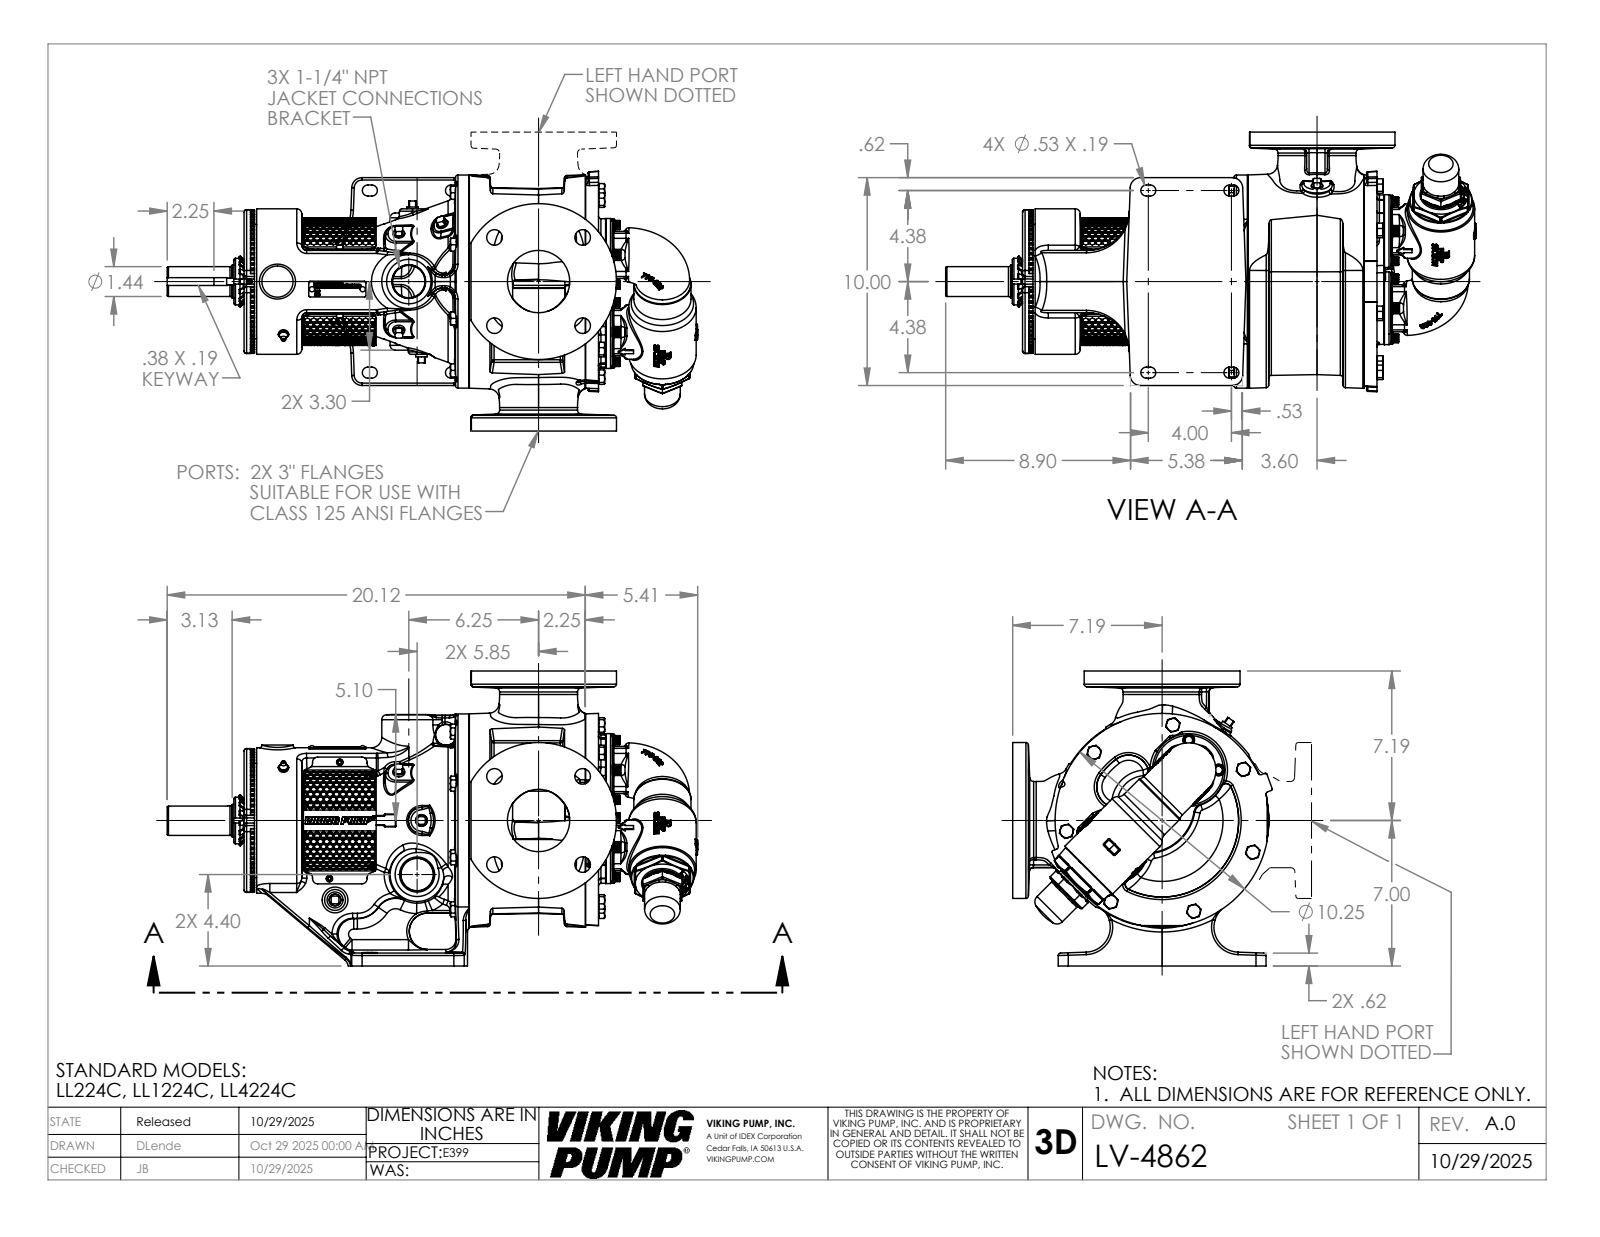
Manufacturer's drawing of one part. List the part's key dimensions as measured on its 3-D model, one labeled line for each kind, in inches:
Part name (STEP PRODUCT): LV-4862
STEP written by: SolidWorks 2024 (AUTOMOTIVE_DESIGN)
Units: inches
Bodies: 1 solid, 5315 faces (1761 planar, 1072 cylindrical, 2482 other)
Overall size (bounding box): 25.53 × 14.19 × 12.492
Volume: 1 055 in³ · Surface area: 1 479 in²
Round holes (diameter × count): ⌀0.406 ×8, ⌀0.41 ×8, ⌀0.75 ×8, ⌀1.094 ×8, ⌀0.199 ×6, ⌀0.25 ×6, ⌀0.159 ×3, ⌀0.266 ×2, ⌀0.313 ×2, ⌀1.552 ×1, ⌀1.577 ×1, ⌀1.593 ×1
Round bosses / shafts (diameter × count): ⌀0.625 ×8, ⌀0.563 ×8, ⌀0.625 ×7, ⌀0.375 ×4, ⌀0.375 ×4, ⌀0.437 ×3, ⌀0.312 ×3, ⌀7.5 ×2
Partial cylindrical surfaces — rounded edges, fillets, slot ends (radius × count): R0.063 ×109, R0.12 ×83, R0.069 ×74, R0.03 ×36, R0.5 ×26, R0.24 ×16, R0.45 ×16, R0.06 ×12
Main face-to-face distances: 14.19, 14.307, 3.537, 10.77, 0.5, 2.25, 1.5, 2.143, 5.68, 16.45
Hole centre spacings: 3, 4.243, 1.375, 3.609, 1.709, 2.18, 4.446, 4.625
